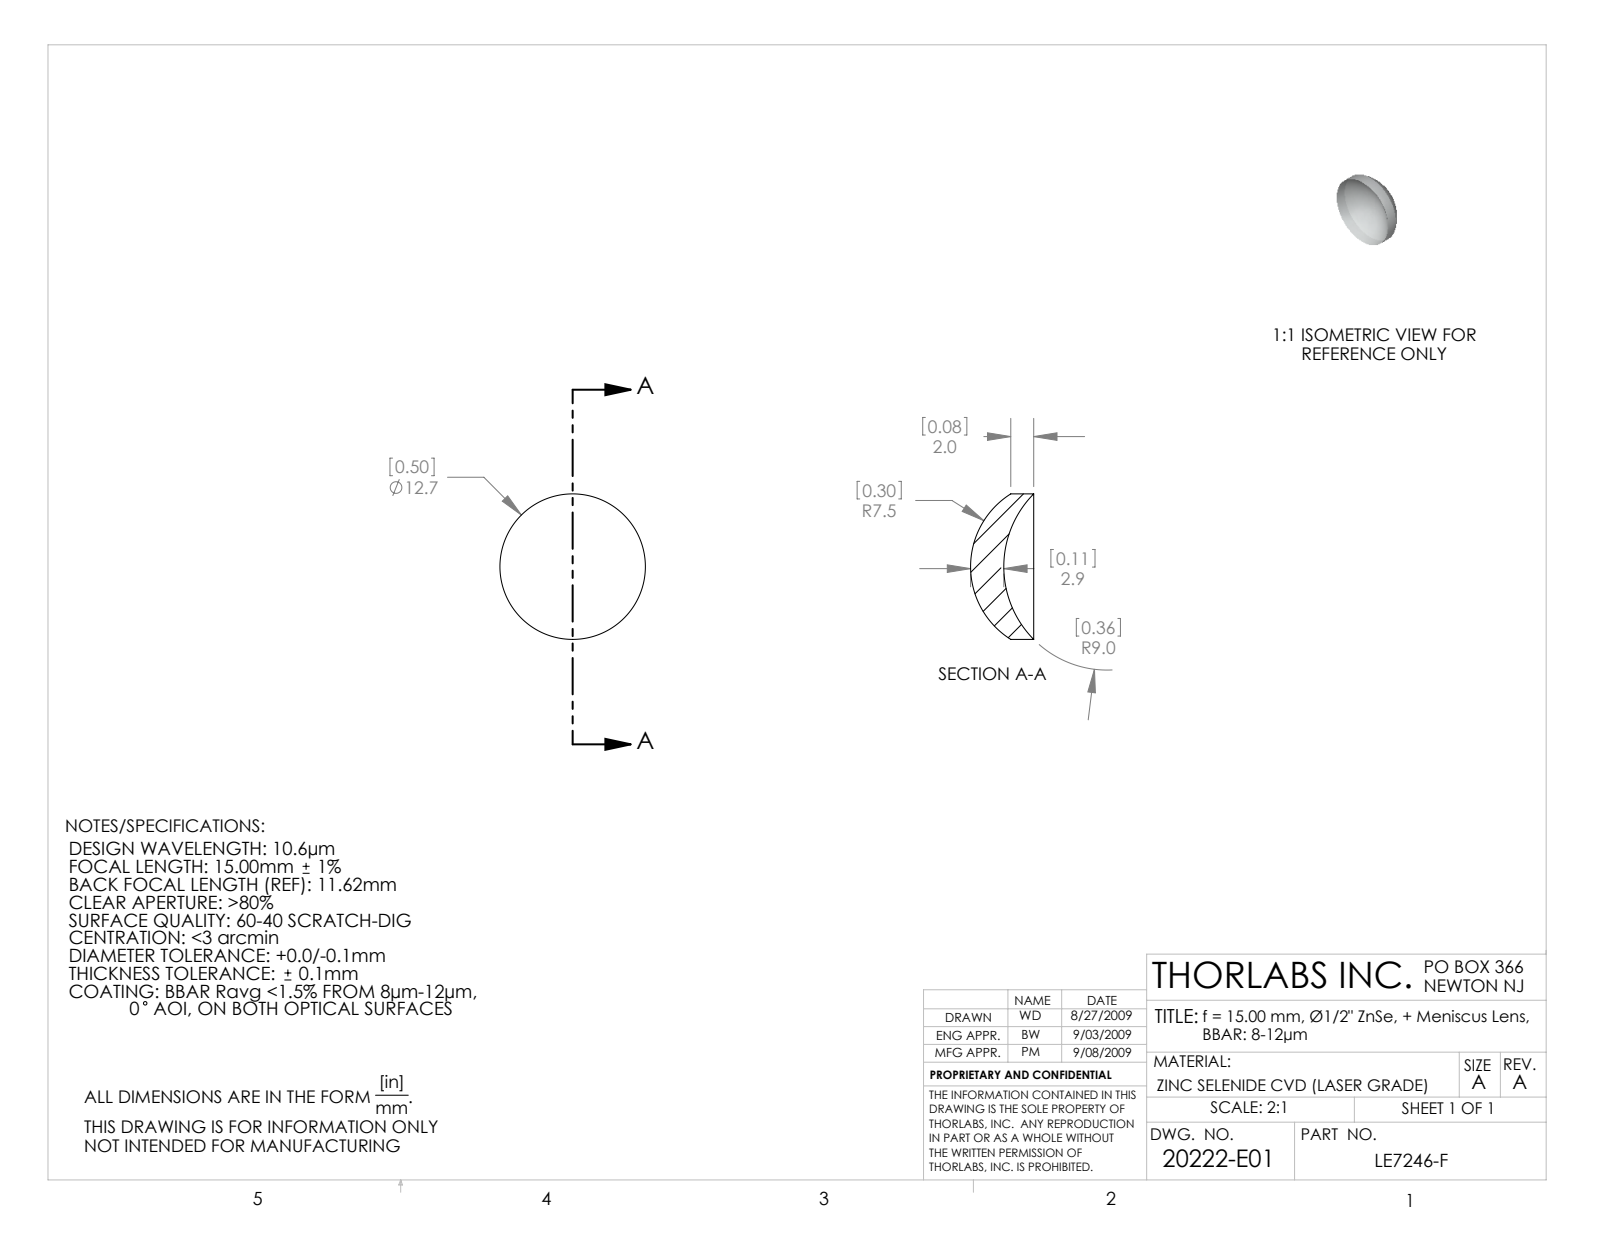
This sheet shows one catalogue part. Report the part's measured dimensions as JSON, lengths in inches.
{"part_name": "20222-E0W", "step_written_by": "SolidWorks 2007 (CONFIG_CONTROL_DESIGN)", "units": "inches", "bodies": {"solids": 1, "faces": 6, "planar": 0, "cylindrical": 2, "other": 4}, "overall_size": [0.5, 0.5, 0.217], "volume_in3": 0.02, "surface_area_in2": 0.609, "round_bosses_or_shafts": [[0.5, 1]]}
